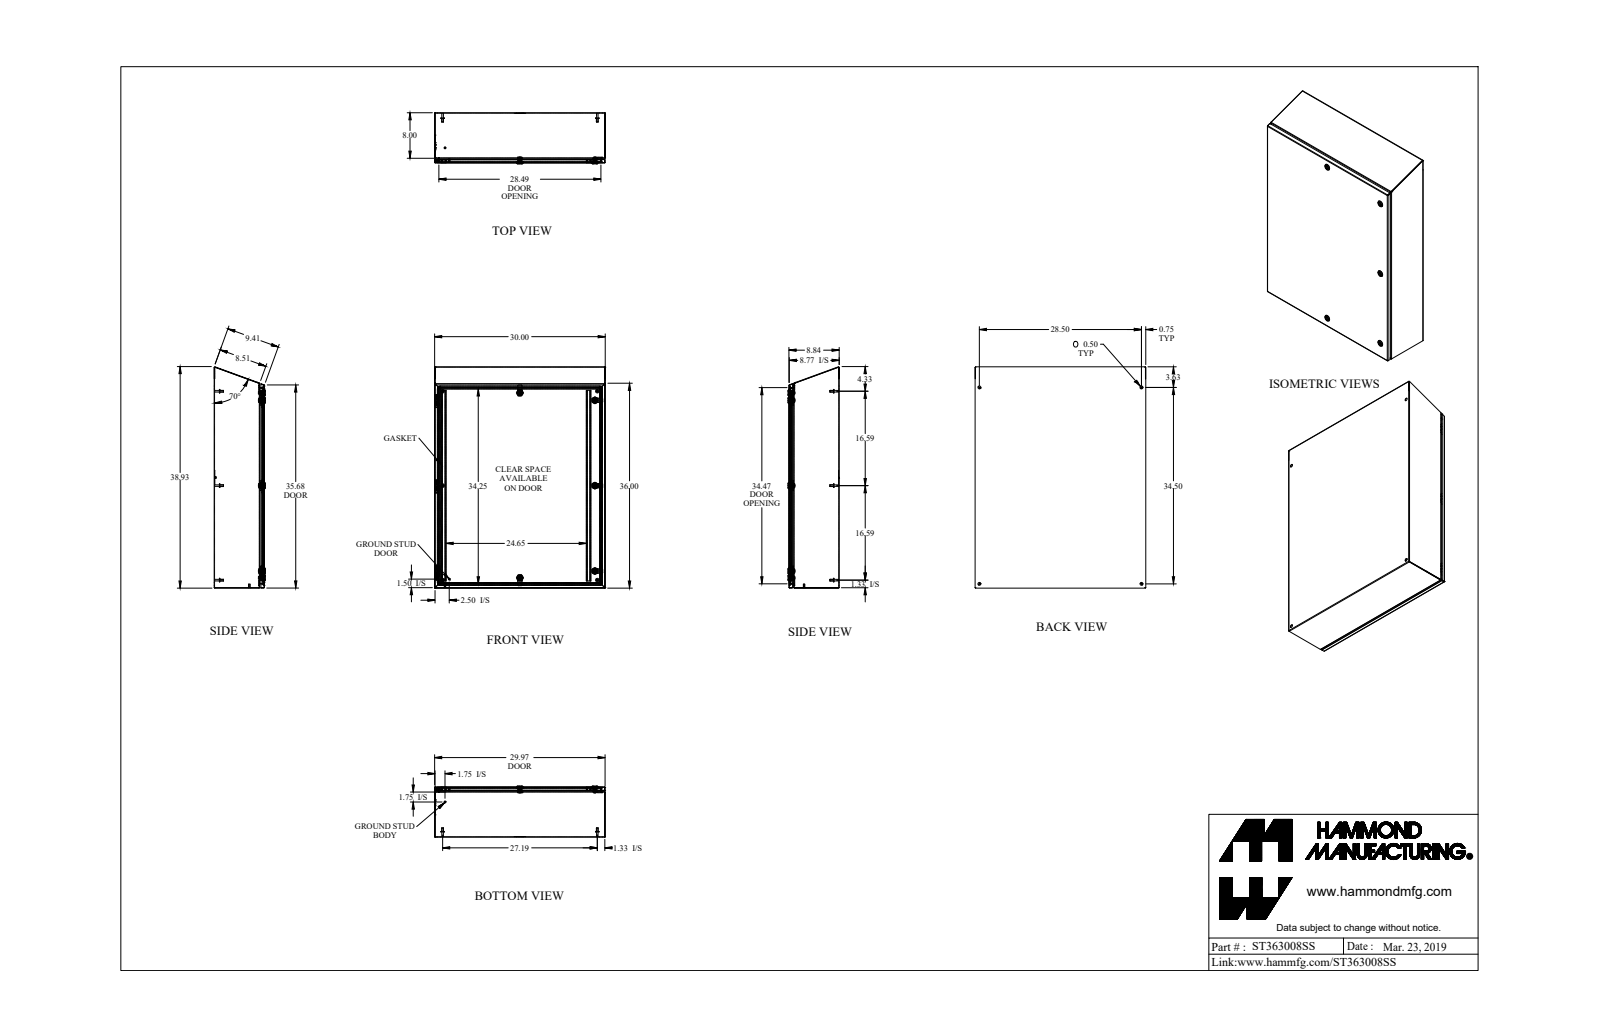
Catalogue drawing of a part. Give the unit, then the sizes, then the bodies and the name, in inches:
Units: inches
Overall size (bounding box): 38.883 × 30 × 8.997
Round holes (diameter × count): ⌀0.5 ×9, ⌀0.197 ×5, ⌀0.387 ×5, ⌀0.63 ×5, ⌀0.768 ×5, ⌀0.172 ×1, ⌀0.24 ×1, ⌀0.242 ×1
Round bosses / shafts (diameter × count): ⌀0.625 ×9, ⌀0.313 ×8, ⌀0.275 ×6, ⌀1.1 ×5, ⌀0.785 ×5, ⌀0.525 ×5, ⌀0.236 ×5, ⌀0.625 ×2
Partial cylindrical surfaces — rounded edges, fillets, slot ends (radius × count): R0.036 ×20, R0.108 ×20, R0.01 ×12, R0.048 ×12, R0.25 ×11, R0.125 ×10, R0.006 ×6, R0.062 ×6
Main face-to-face distances: 0.072, 8.765, 8.693, 8.837, 29.928, 29.856, 30, 0.837, 7.928, 0.909
Hole centre spacings: 2.493, 15, 17.283, 27.518, 28.5, 32.268, 32.4, 34.5
Volume: 278.4 in³ · Surface area: 7 784 in²
Bodies: 48 solids, 1269 faces (713 planar, 378 cylindrical, 178 other)
Part name (STEP PRODUCT): ST363008SS
STEP written by: SolidWorks 2018 (AUTOMOTIVE_DESIGN)
